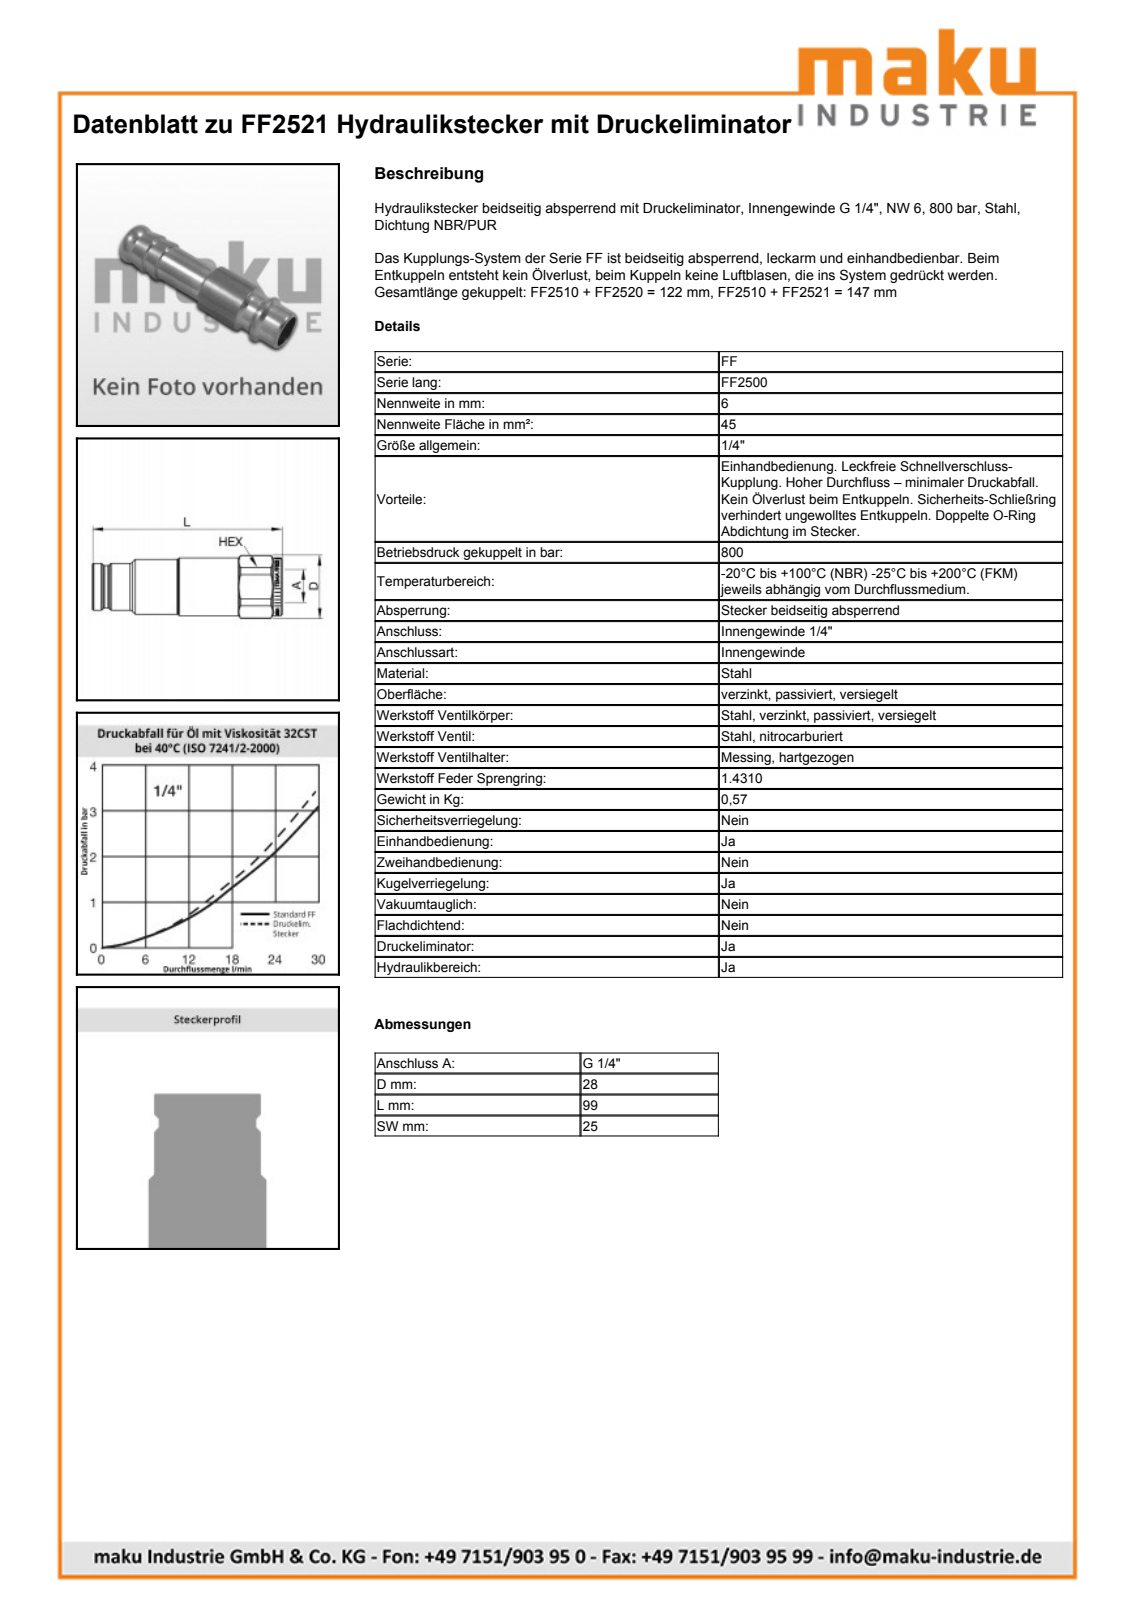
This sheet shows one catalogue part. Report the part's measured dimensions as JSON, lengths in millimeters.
{"part_name": "FF2521", "step_written_by": "SolidWorks 2009 (AUTOMOTIVE_DESIGN)", "units": "millimeters", "bodies": {"solids": 1, "faces": 69, "planar": 13, "cylindrical": 20, "other": 36}, "overall_size": [99.2, 30, 27], "volume_mm3": 49161, "surface_area_mm2": 9624, "round_holes": [[11.44, 1]], "round_bosses_or_shafts": [[26.8, 1], [23.5, 1], [21.89, 1], [19.2, 1], [16.5, 1]], "partial_cylinders_radius": [[15, 1]], "face_to_face_distances": [27, 99.2, 56, 43.2, 12.37, 43.63, 86.83, 99.16, 86.79, 43.16]}
